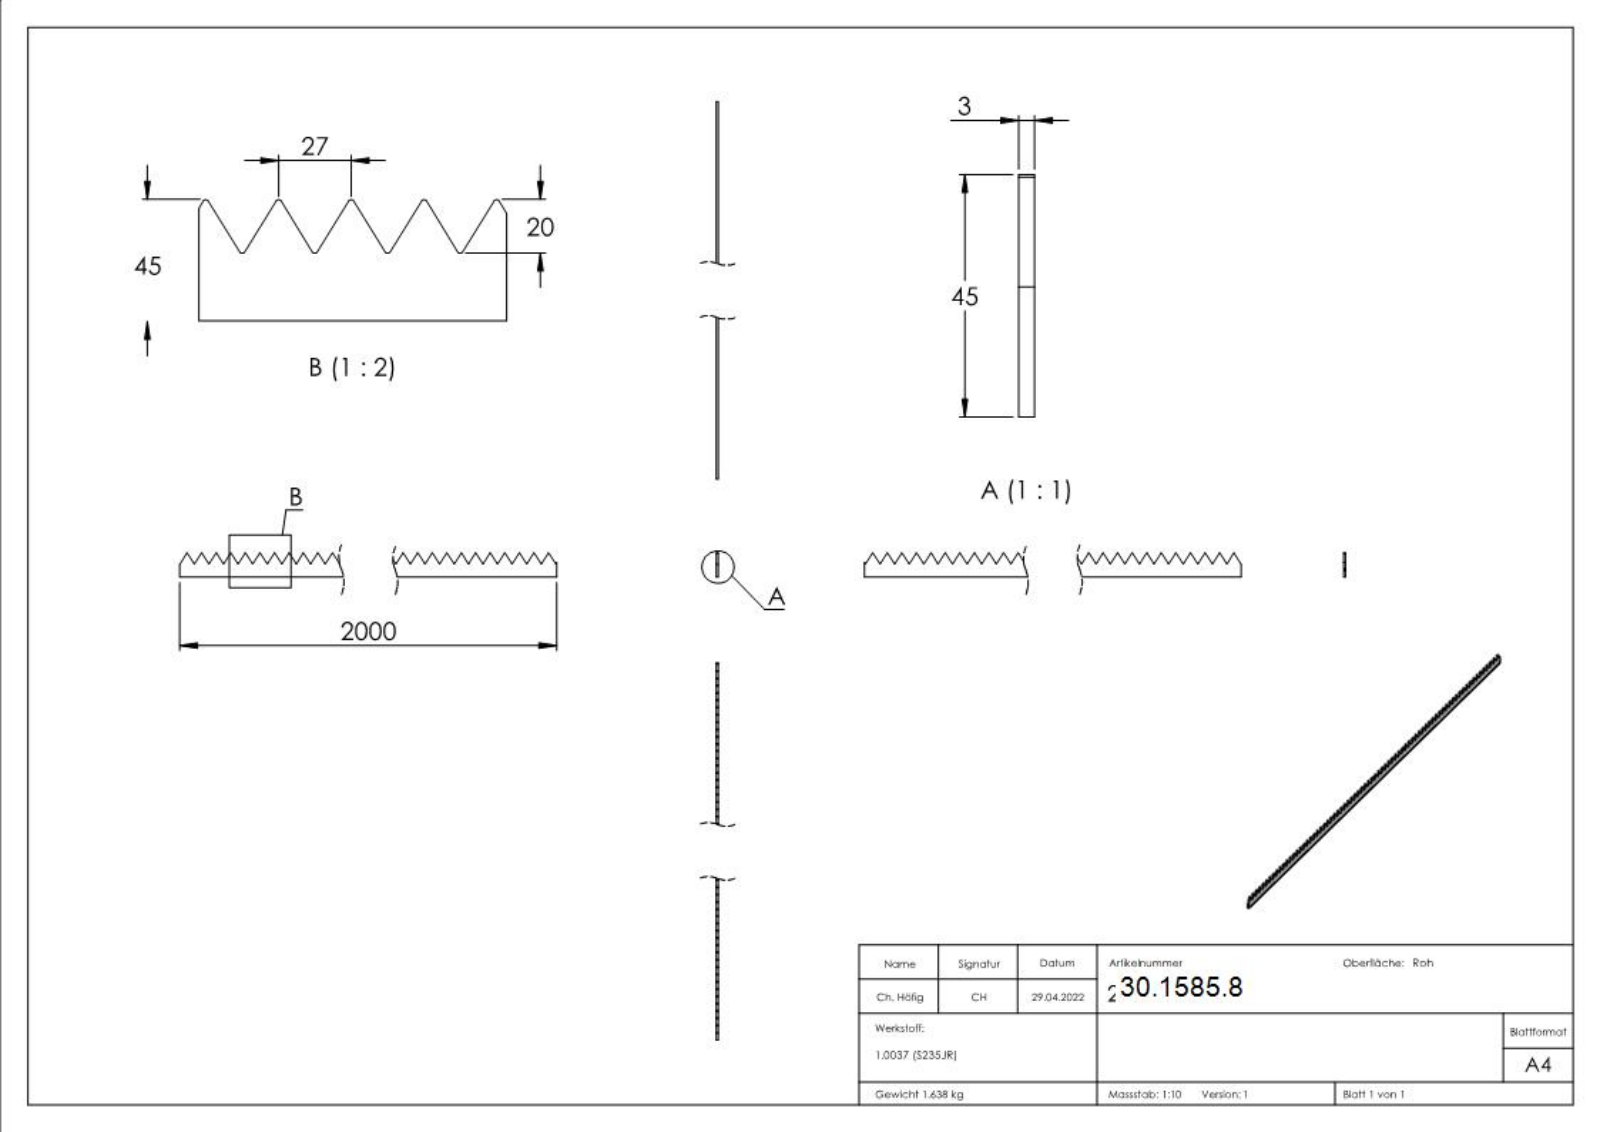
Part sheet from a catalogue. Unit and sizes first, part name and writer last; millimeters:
Units: millimetres
Overall size (bounding box): 2000 × 45 × 3
Partial cylindrical surfaces — rounded edges, fillets, slot ends (radius × count): R1 ×148
Main face-to-face distances: 3, 160.7, 229.57, 275.49, 321.4, 114.79, 711.67, 91.83, 68.87, 528.01
Volume: 209 944 mm³ · Surface area: 156 996 mm²
Bodies: 1 solid, 470 faces (233 planar, 148 cylindrical, 89 other)
Part name (STEP PRODUCT): 2080
STEP written by: SolidWorks 2018 (CONFIG_CONTROL_DESIGN)
